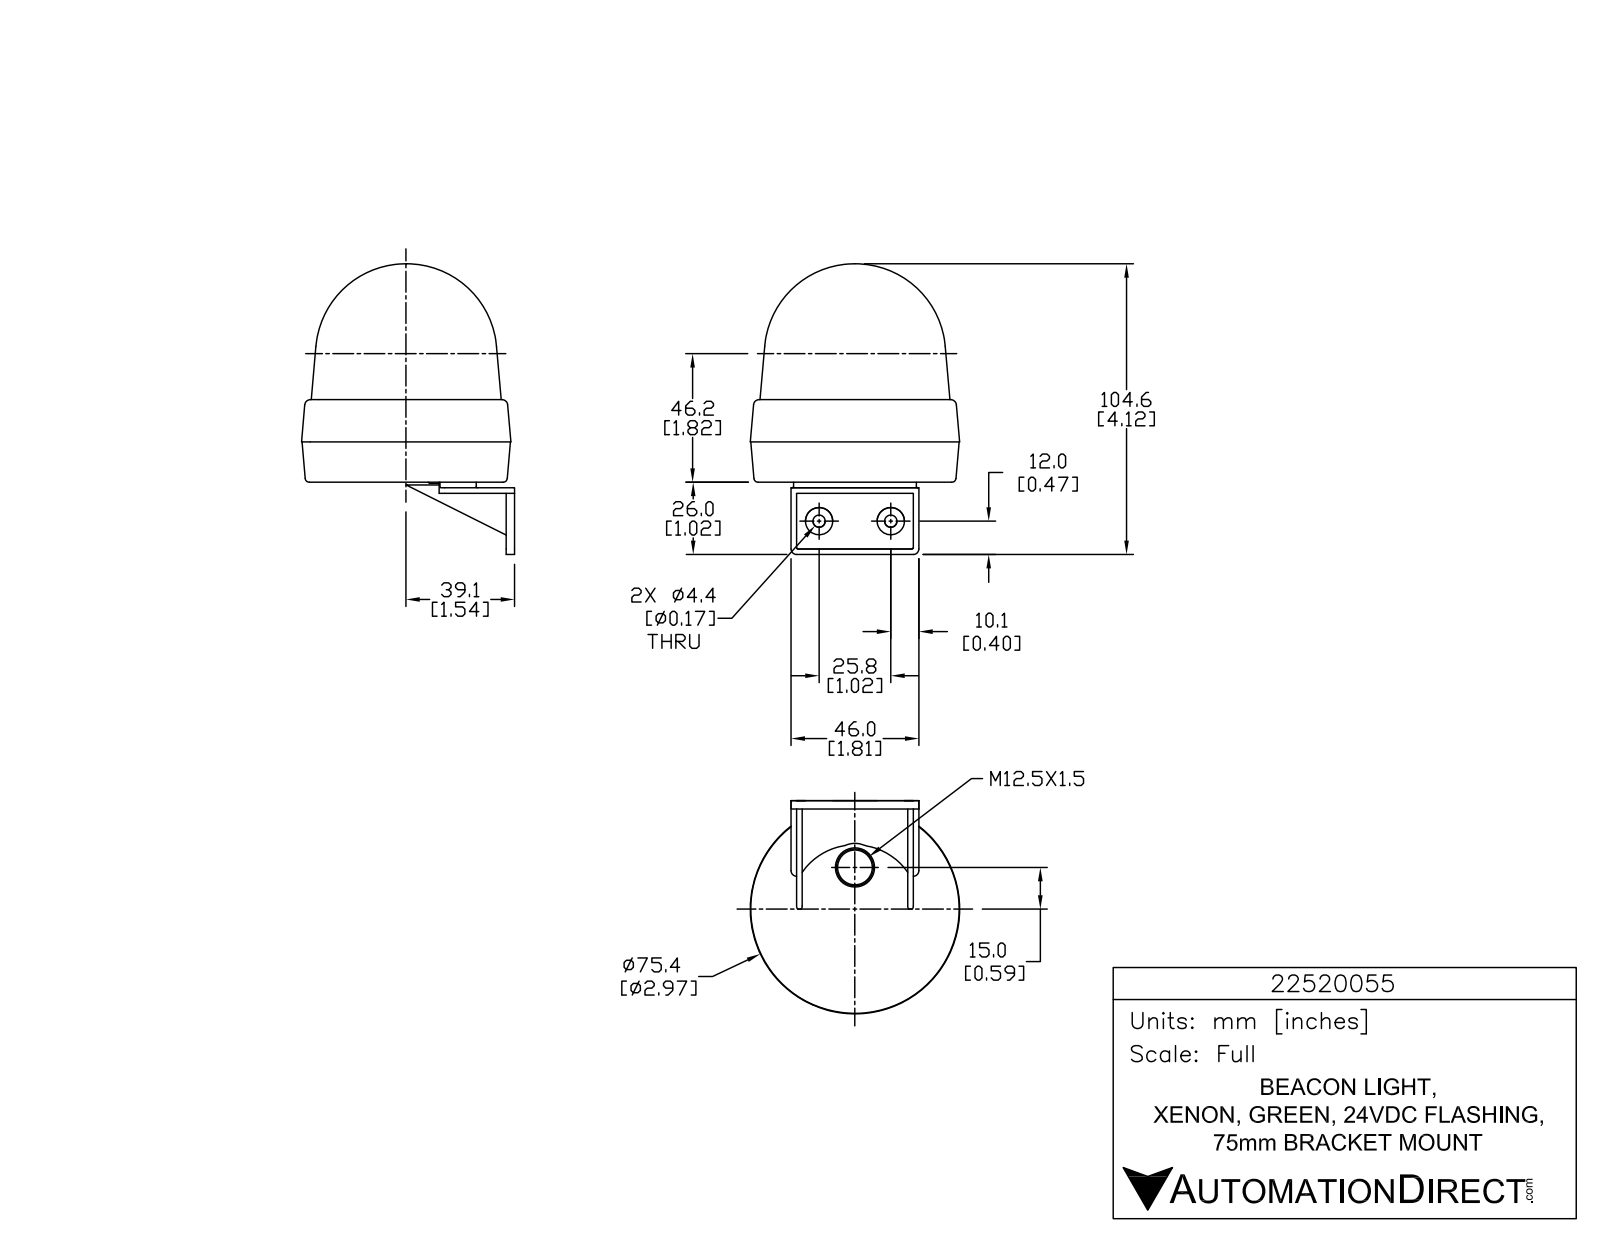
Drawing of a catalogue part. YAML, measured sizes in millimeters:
part_name: "22520055"
step_written_by: "SolidWorks 2015 (AUTOMOTIVE_DESIGN)"
units: millimeters
bodies: {solids: 1, faces: 819, planar: 549, cylindrical: 180, other: 90}
overall_size: [104.6, 82.6, 75.4]
volume: 262500
surface_area: 27080
round_holes:
  - {diameter: 1.5, count: 3}
  - {diameter: 4.4, count: 2}
round_bosses_or_shafts:
  - {diameter: 8.6, count: 3}
  - {diameter: 2.1, count: 3}
  - {diameter: 9.8, count: 2}
partial_cylinders:
  - {radius: 0.1, count: 9}
  - {radius: 0.1, count: 6}
  - {radius: 0.3, count: 6}
  - {radius: 0.3, count: 6}
  - {radius: 0.3, count: 6}
  - {radius: 0.5, count: 6}
  - {radius: 5, count: 6}
  - {radius: 2, count: 4}
face_to_face_distances: [2, 4, 40, 1, 3, 42, 38, 2, 42, 44]
hole_center_spacings: [25.8]
